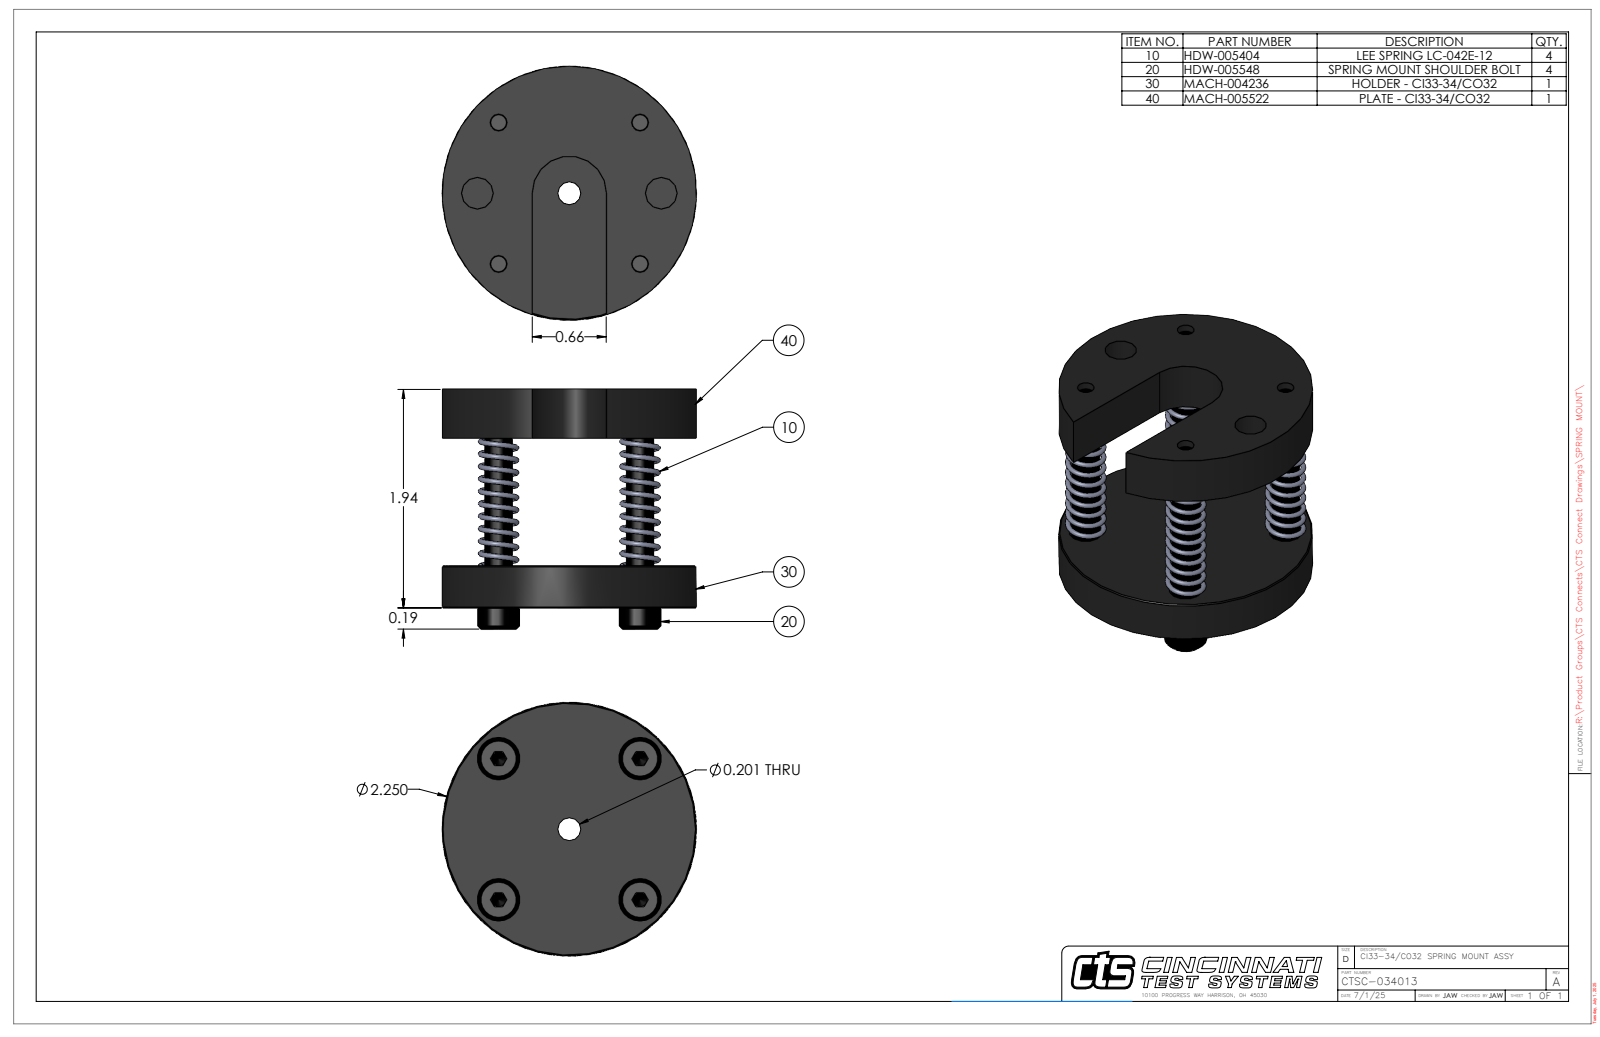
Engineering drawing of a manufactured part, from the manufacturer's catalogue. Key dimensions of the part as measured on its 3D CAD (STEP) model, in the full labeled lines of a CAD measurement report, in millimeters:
Part name (STEP PRODUCT): MACH-005522 (PLATE - CI33-34,CO32); HDW-005548 (.25 X 1.5 SHSS)_SHSSCREW 0.25x1.5-N; HDW-005404 (LEE SPRING LC-042E-12); MACH-004236 (HOLDER - CI33-34,CO32) (+1 more)
STEP written by: SolidWorks 2023 (AUTOMOTIVE_DESIGN)
Units: millimetres
Bodies: 10 solids, 222 faces (86 planar, 68 cylindrical, 68 other)
Overall size (bounding box): 57.2 × 57.2 × 54
Volume: 50 700 mm³ · Surface area: 23 170 mm²
Round holes (diameter × count): ⌀3.8 ×4, ⌀7.5 ×4, ⌀7.1 ×2, ⌀5.1 ×1
Round bosses / shafts (diameter × count): ⌀9.5 ×4, ⌀6.3 ×4, ⌀5.8 ×4, ⌀4.8 ×4, ⌀3.4 ×4, ⌀57.2 ×1
Partial cylindrical surfaces — rounded edges, fillets, slot ends (radius × count): R8.3 ×1
Main face-to-face distances: 9.5, 38.1, 28.6, 11.1, 39.7, 49.2, 16.7, 54, 42.9, 14.3
Hole centre spacings: 31.8, 16.6, 22.5, 39.8, 20.7, 22.5, 31.8, 39.8
